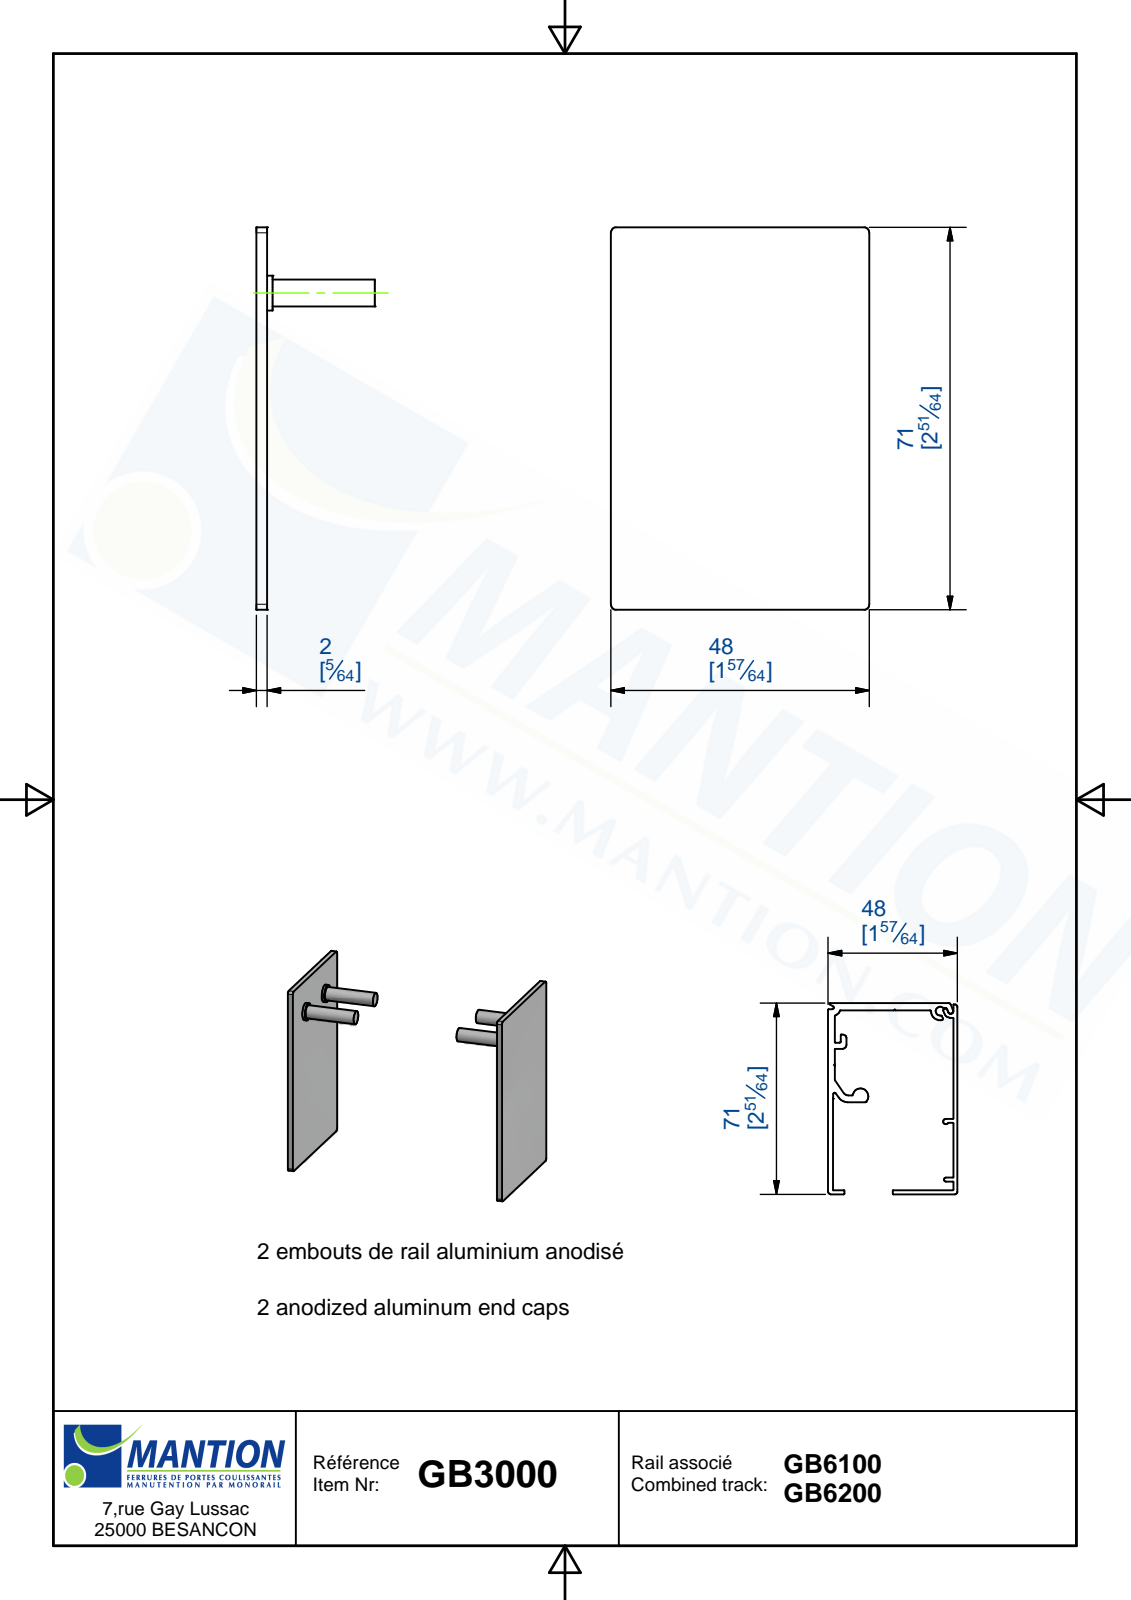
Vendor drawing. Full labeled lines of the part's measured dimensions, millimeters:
Part name (STEP PRODUCT): GB3000; 23313; 23318; 23337
STEP written by: Autodesk Inventor 2019 (AUTOMOTIVE_DESIGN)
Units: millimetres
Bodies: 6 solids, 52 faces (28 planar, 20 cylindrical, 4 other)
Overall size (bounding box): 126 × 71 × 22
Volume: 15 260 mm³ · Surface area: 16 121 mm²
Round bosses / shafts (diameter × count): ⌀6.5 ×4, ⌀5 ×4, ⌀0.75 ×4
Partial cylindrical surfaces — rounded edges, fillets, slot ends (radius × count): R1 ×8
Main face-to-face distances: 2, 48, 78, 71, 126, 30, 20, 22, 19, 1
